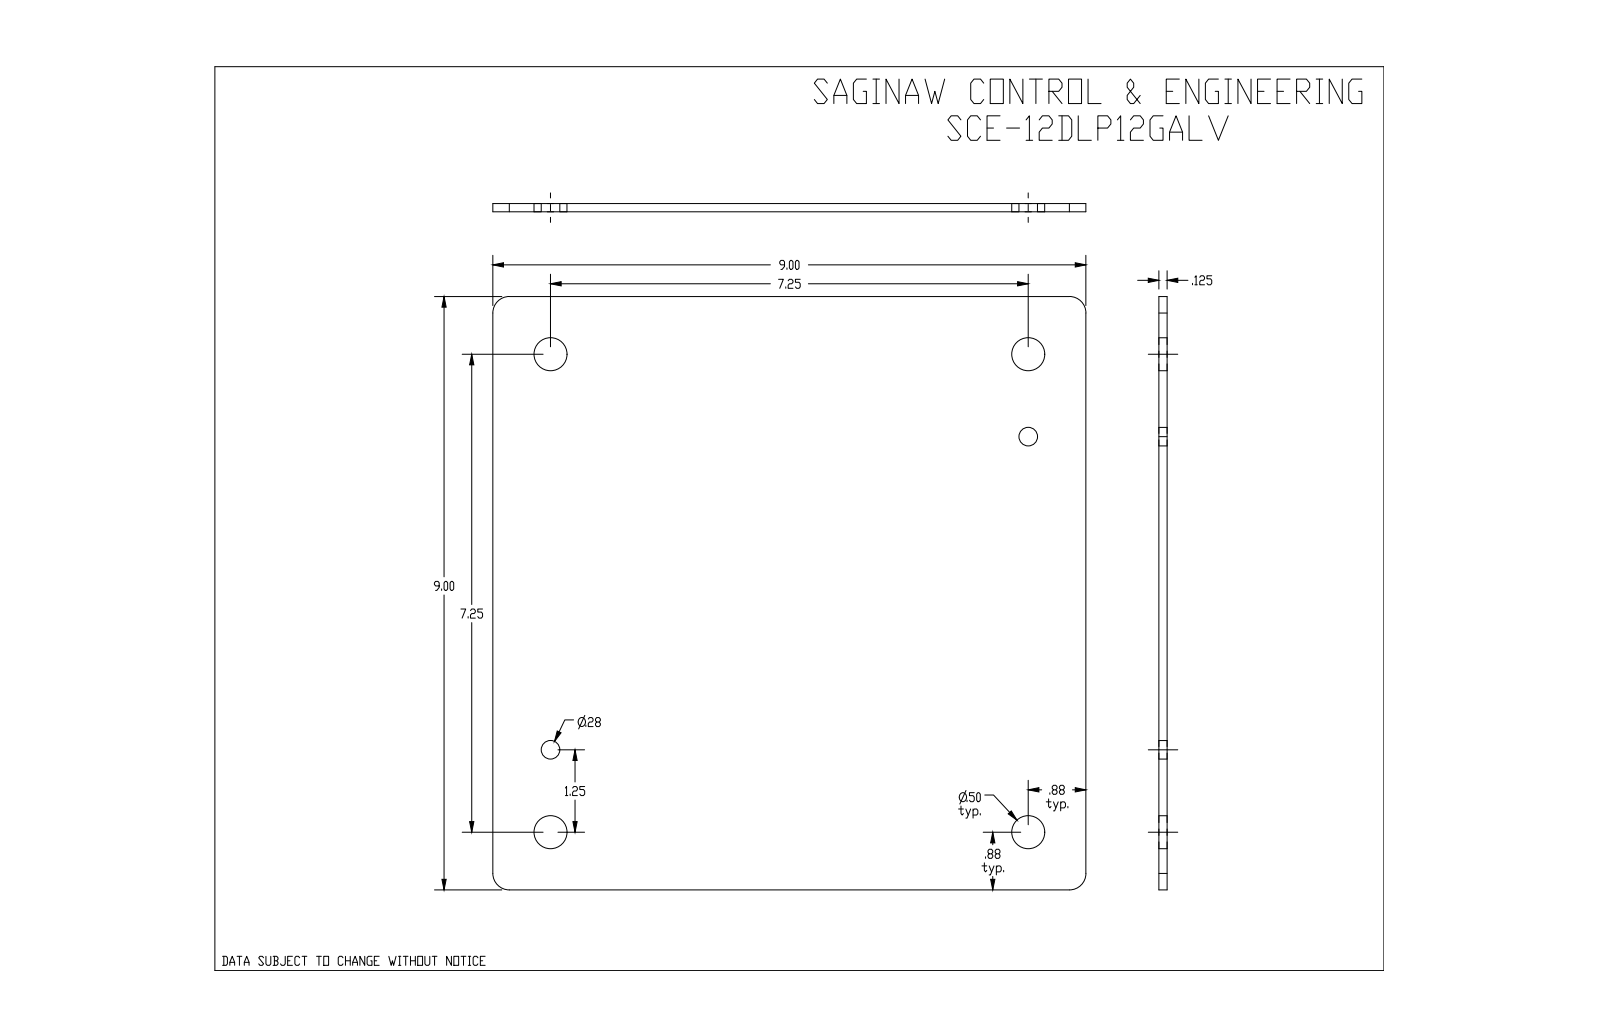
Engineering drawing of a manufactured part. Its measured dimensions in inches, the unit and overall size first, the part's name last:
Units: inches
Overall size (bounding box): 9 × 9 × 0.125
Round holes (diameter × count): ⌀0.5 ×4, ⌀0.281 ×1, ⌀0.281 ×1
Partial cylindrical surfaces — rounded edges, fillets, slot ends (radius × count): R0.25 ×4
Main face-to-face distances: 0.125, 9
Hole centre spacings: 7.25, 1.25, 6, 7.357, 9.41, 10.252, 8.667
Volume: 10 in³ · Surface area: 165.5 in²
Bodies: 1 solid, 16 faces (6 planar, 10 cylindrical, 0 other)
Part name (STEP PRODUCT): SCE-12DLP12GALV
STEP written by: SolidWorks 2019 (CONFIG_CONTROL_DESIGN)
